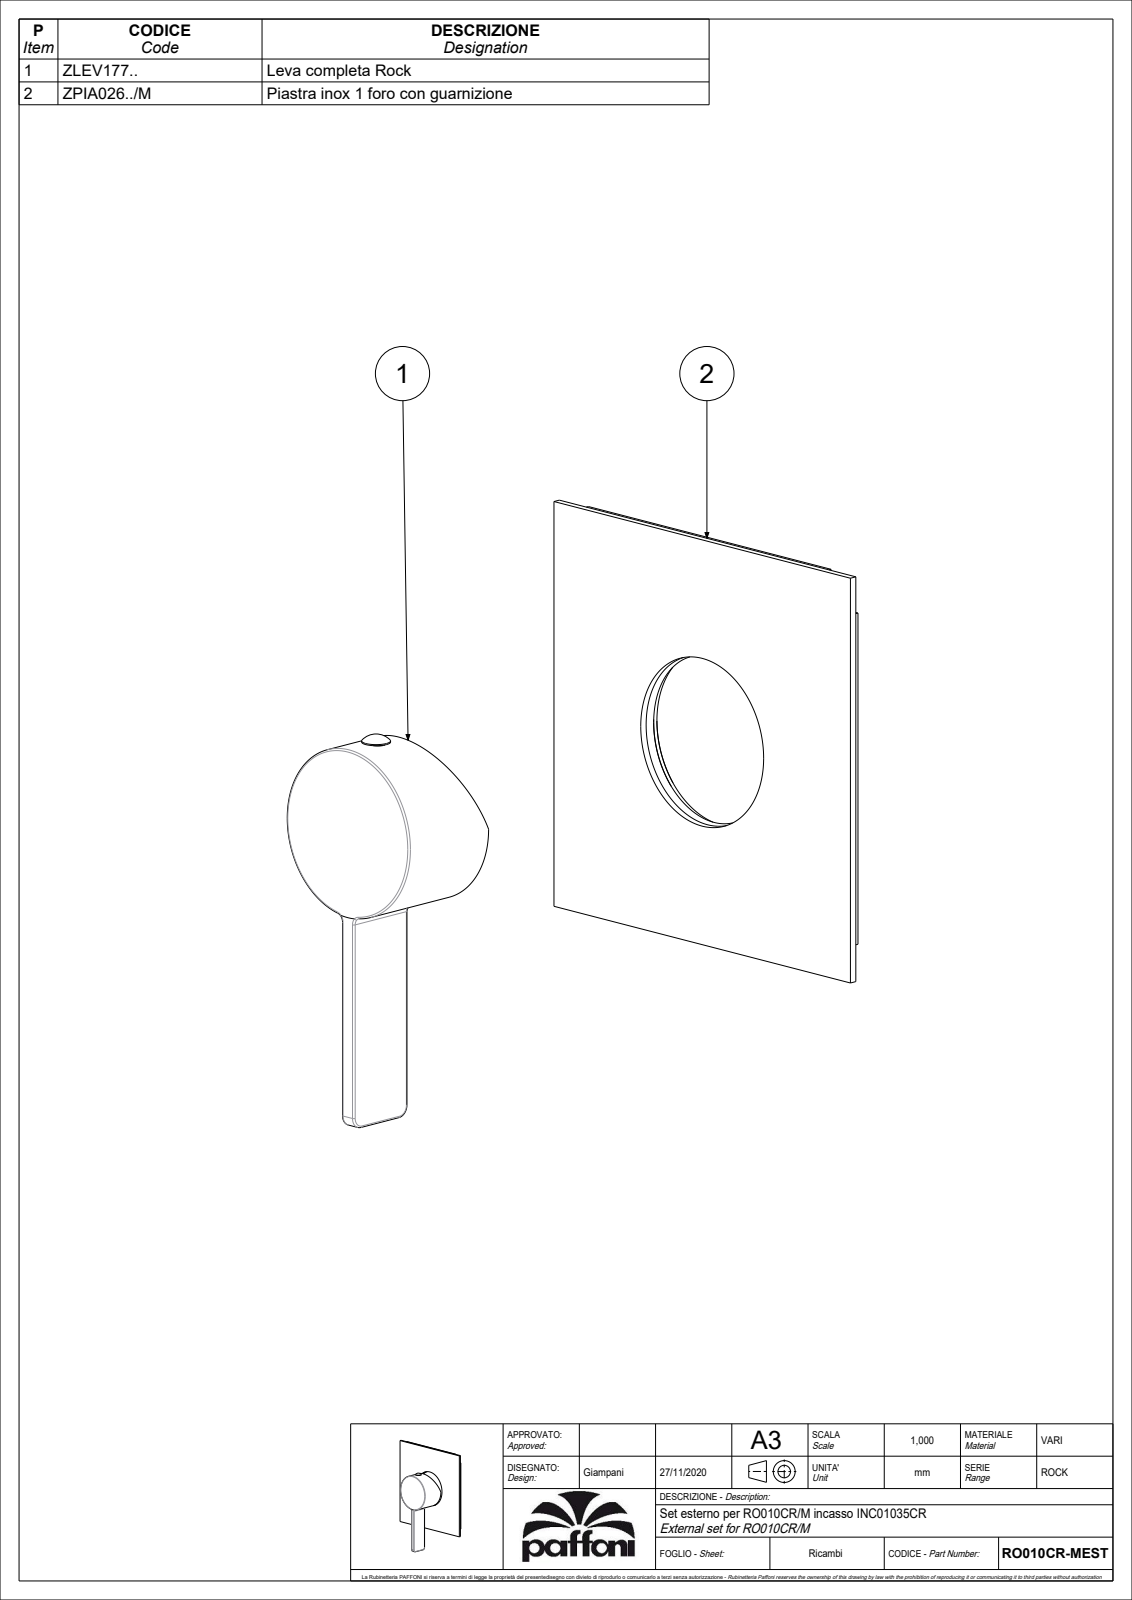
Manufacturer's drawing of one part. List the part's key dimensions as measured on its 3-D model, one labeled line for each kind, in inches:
Part name (STEP PRODUCT): RO010CR-MEST
STEP written by: CREO PARAMETRIC BY PTC INC, 2020044 (CONFIG_CONTROL_DESIGN)
Units: inches
Bodies: 2 solids, 167 faces (74 planar, 45 cylindrical, 48 other)
Overall size (bounding box): 5.315 × 4.331 × 1.555
Volume: 2.802 in³ · Surface area: 61.96 in²
Round holes (diameter × count): ⌀0.118 ×1, ⌀1.795 ×1, ⌀1.874 ×1, ⌀2.012 ×1
Round bosses / shafts (diameter × count): ⌀2.15 ×1, ⌀1.791 ×1, ⌀0.299 ×1, ⌀0.217 ×1, ⌀0.197 ×1
Partial cylindrical surfaces — rounded edges, fillets, slot ends (radius × count): R0.02 ×9, R0.012 ×2, R0.059 ×2, R0.079 ×2, R0.118 ×2, R0.138 ×1
Main face-to-face distances: 0.079, 0.031, 0.11, 0.177, 1.213, 1.181, 1.102, 2.077, 2.254, 4.331
